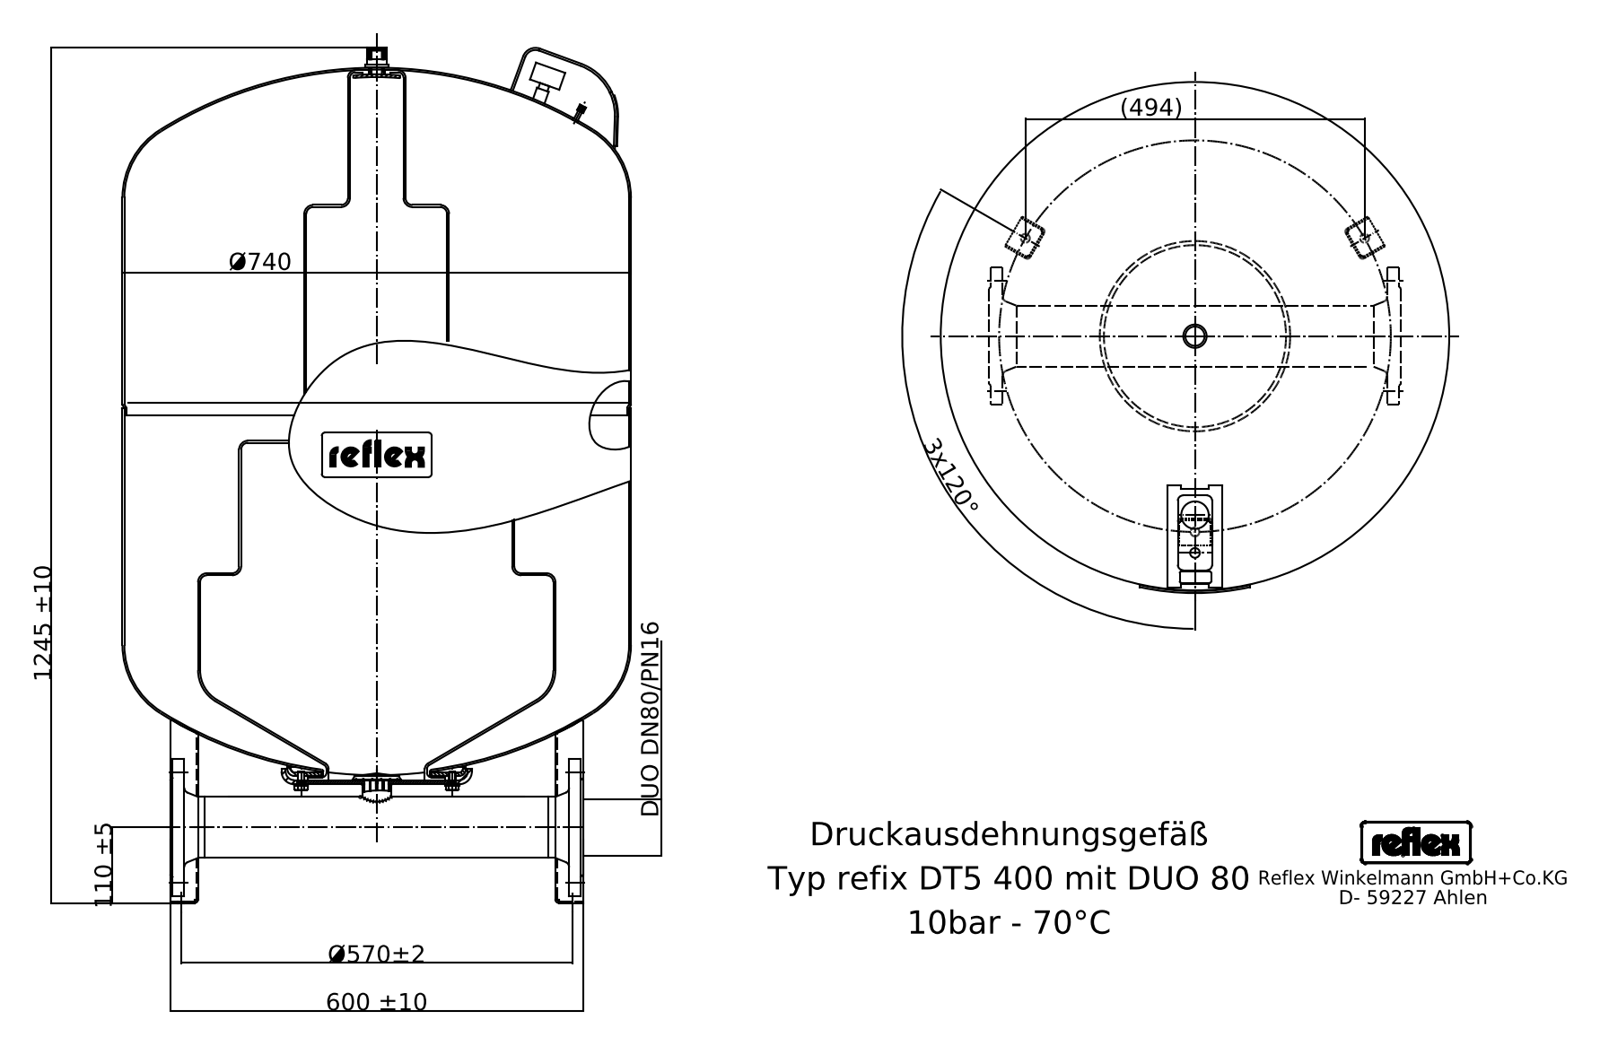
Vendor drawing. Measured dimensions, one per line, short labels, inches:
written by: Mechanical Desktop 2008 (CONFIG_CONTROL_DESIGN)
unit: in
bodies: 23 solids, 529 faces (225 planar, 188 cylindrical, 116 other)
size: 49.016 × 29.134 × 29.134
volume: 23 960 in³; area: 8 147 in²
holes: 8× ⌀0.748, 3× ⌀0.528, 1× ⌀0.098, 1× ⌀0.276, 1× ⌀0.315, 1× ⌀0.449, 1× ⌀3.5, 1× ⌀6.181, 1× ⌀9.843
bosses: 9× ⌀0.394, 1× ⌀29.134, 1× ⌀10.236, 1× ⌀9.055, 1× ⌀7.874, 1× ⌀2.441, 1× ⌀1.669, 1× ⌀1.339
rounds: 15× R0.039, 15× R0.098, 15× R0.197, 4× R0.221, 3× R0.089, 2× R0.151, 2× R0.266, 2× R0.315
face distances: 25.669, 0.098, 1.87, 7.717, 33.386, 0.236, 7.953, 33.622, 1.969, 1.772
hole spacings: 3.15, 4.454, 2.41, 2.411, 5.819, 5.82, 6.299, 11.22
